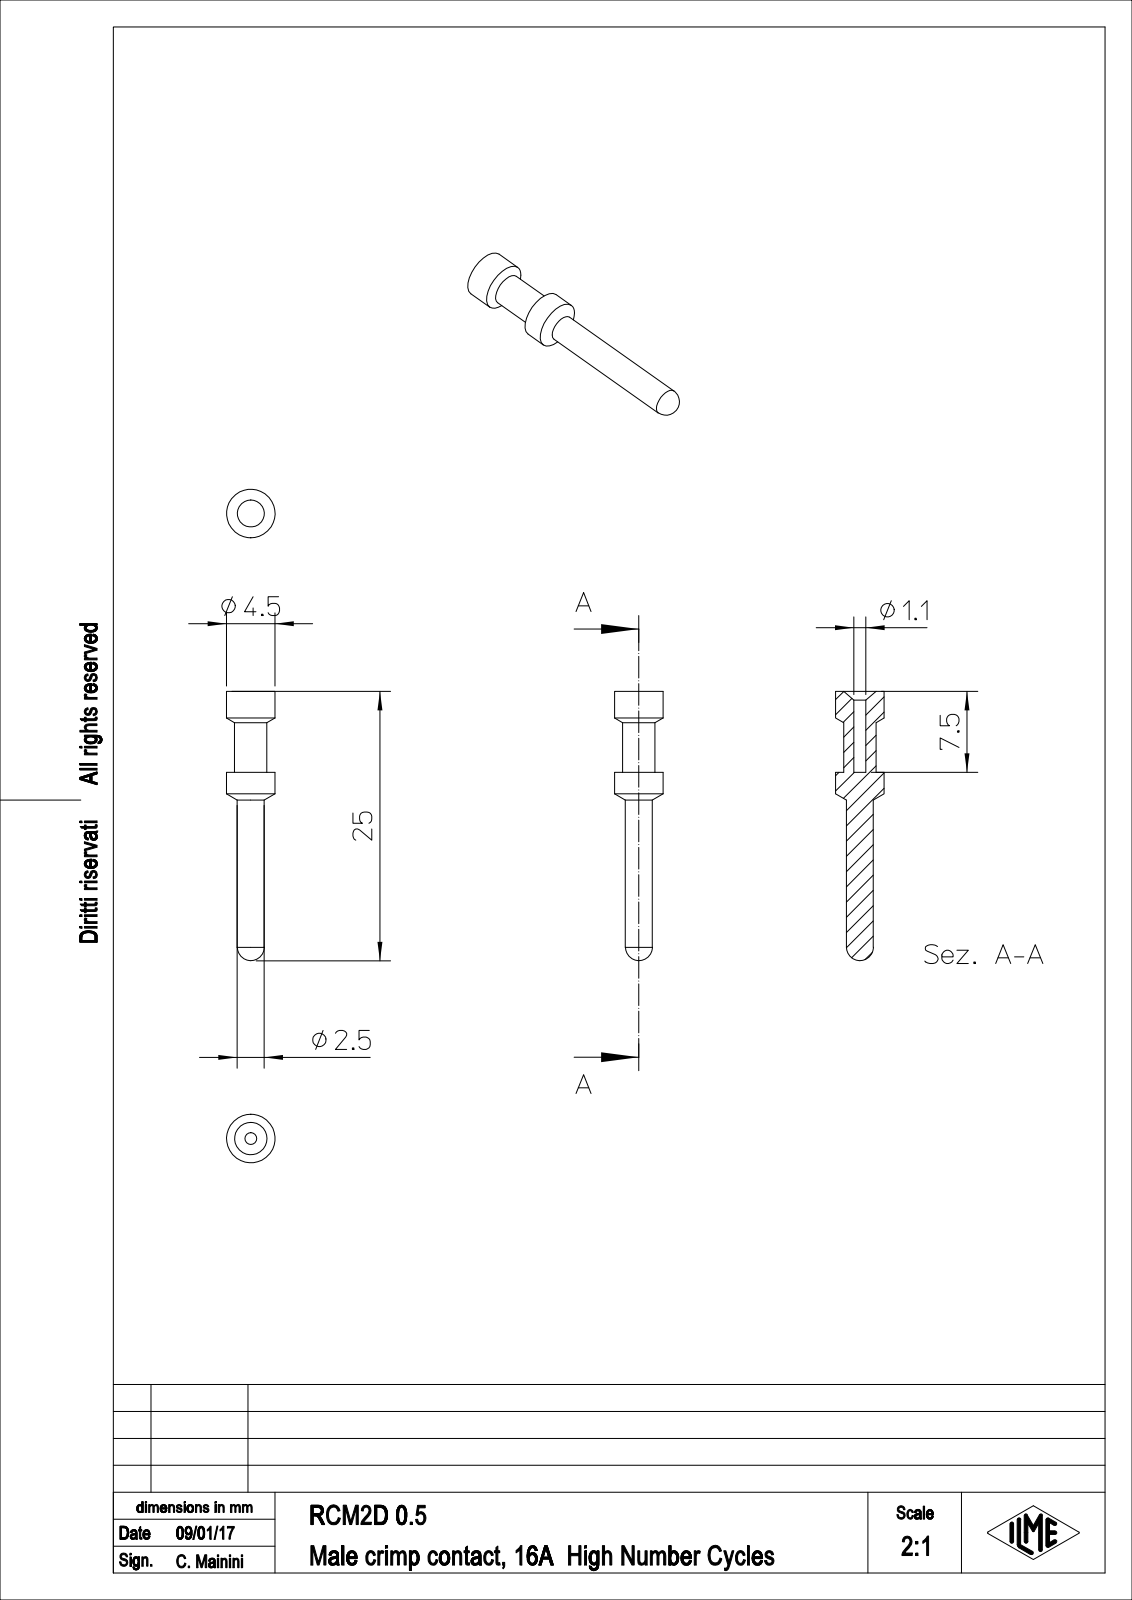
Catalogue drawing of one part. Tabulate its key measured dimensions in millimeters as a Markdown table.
| quantity | value |
| --- | --- |
| part name | RCM2D_0.5 |
| STEP written by | PTC Creo Elements/Direct Modeling 19.0E 27-Jun-2016 (C) Parametric Technology GmbH (AUTOMOTIVE_DESIGN) |
| units | millimeters |
| bodies | 1 solid, 21 faces (3 planar, 10 cylindrical, 8 other) |
| overall size | 25 × 4.5 × 4.5 |
| volume | 176 mm³ |
| surface area | 296 mm² |
| round holes (diameter × count) | 1.1 × 1 |
| round bosses / shafts (diameter × count) | 4.5 × 1, 3 × 1, 2.5 × 1 |
| main face-to-face distances | 7.5 |
